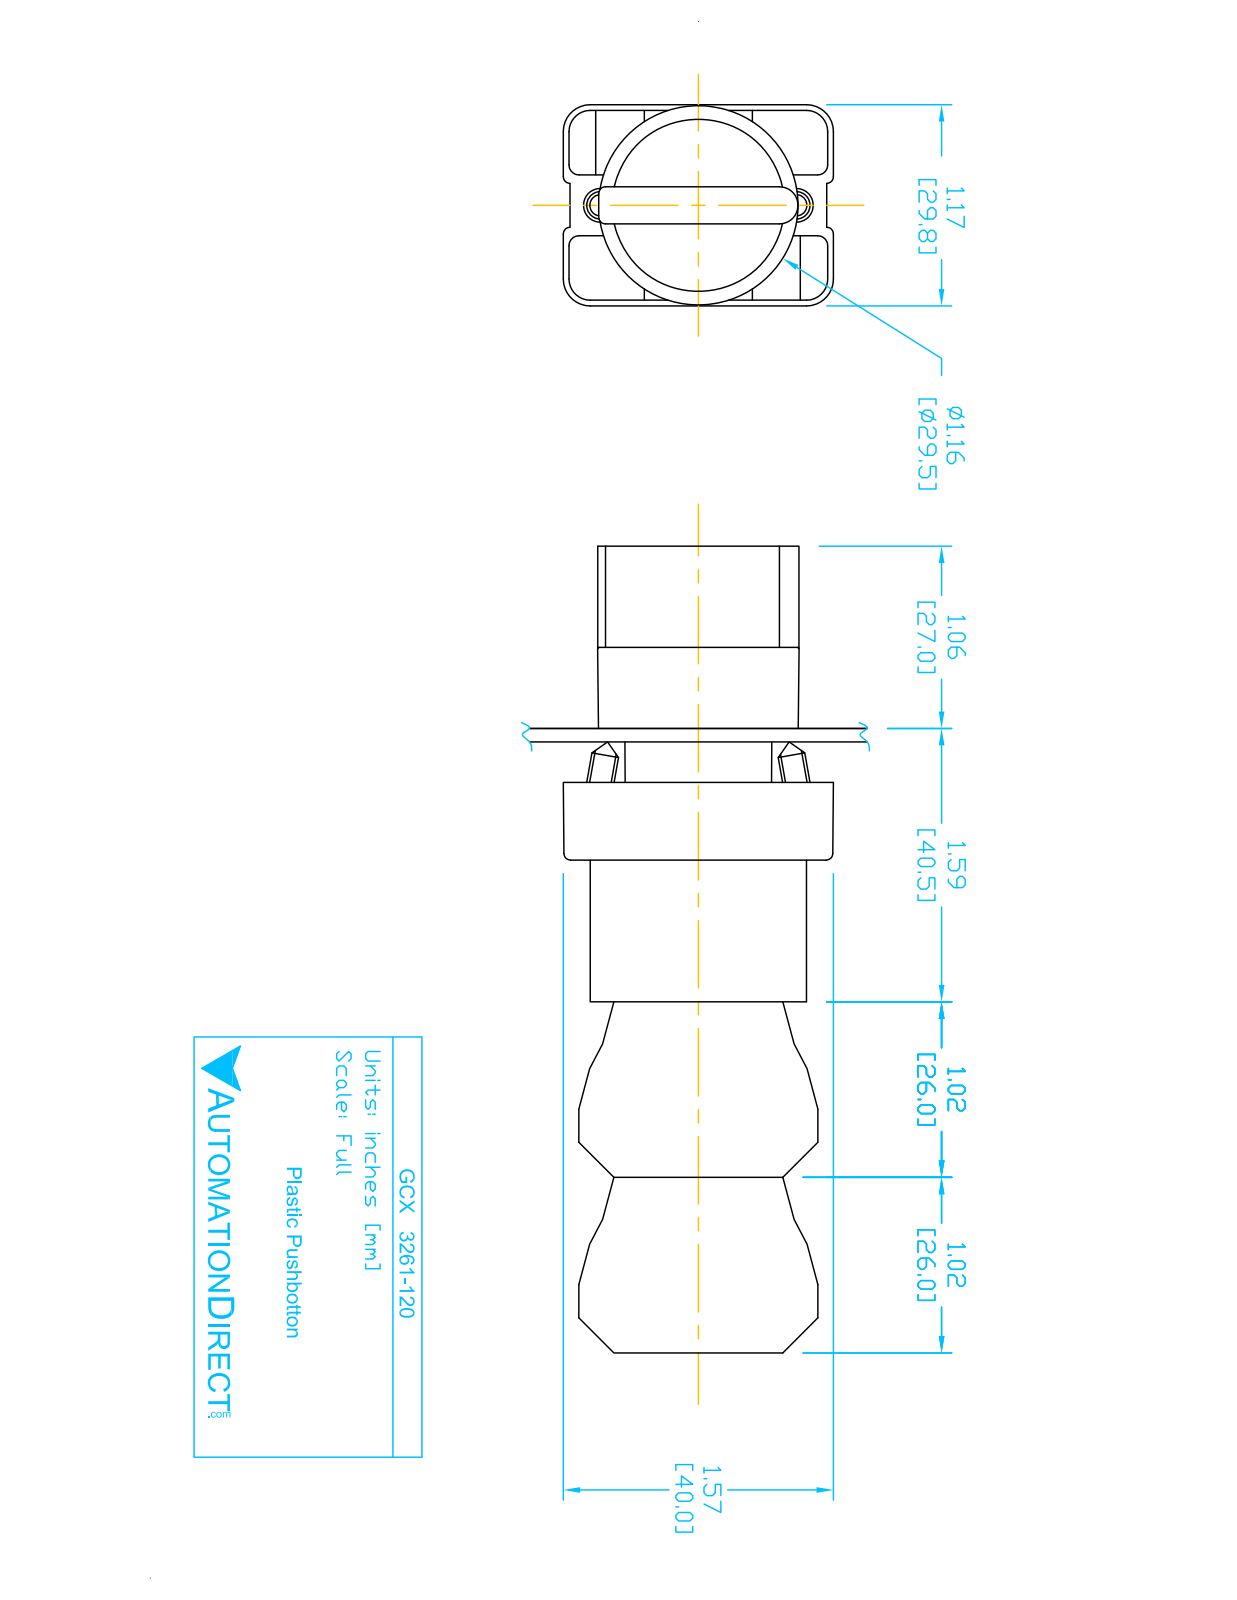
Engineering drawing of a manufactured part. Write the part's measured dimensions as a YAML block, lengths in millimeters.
part_name: "ECX1050; GCX3261 OPERATOR; ecx1040; ecx1030 (+2 more)"
step_written_by: "SolidWorks 2016 (AUTOMOTIVE_DESIGN)"
units: millimeters
bodies: {solids: 11, faces: 724, planar: 488, cylindrical: 193, other: 43}
overall_size: [118.8, 40.2, 29.9]
volume: 77850
surface_area: 38210
round_holes:
  - {diameter: 2, count: 4}
  - {diameter: 2.2, count: 2}
  - {diameter: 3.1, count: 2}
  - {diameter: 3.3, count: 2}
  - {diameter: 5, count: 1}
  - {diameter: 11.9, count: 1}
  - {diameter: 22.3, count: 1}
  - {diameter: 22.6, count: 1}
  - {diameter: 26, count: 1}
round_bosses_or_shafts:
  - {diameter: 4, count: 4}
  - {diameter: 29.8, count: 1}
  - {diameter: 25.5, count: 1}
  - {diameter: 24, count: 1}
  - {diameter: 21.7, count: 1}
  - {diameter: 19.8, count: 1}
  - {diameter: 12.8, count: 1}
partial_cylinders:
  - {radius: 1.5, count: 24}
  - {radius: 1, count: 12}
  - {radius: 3.1, count: 12}
  - {radius: 4, count: 12}
  - {radius: 1, count: 9}
  - {radius: 0.5, count: 2}
  - {radius: 1.6, count: 2}
  - {radius: 2, count: 2}
face_to_face_distances: [14.7, 15.1, 26, 29.7, 0.4, 21, 47, 77.3, 51.3, 30.3]
hole_center_spacings: [6, 25.5, 24.7, 12, 13.7, 13.8, 27.5, 12.3]
